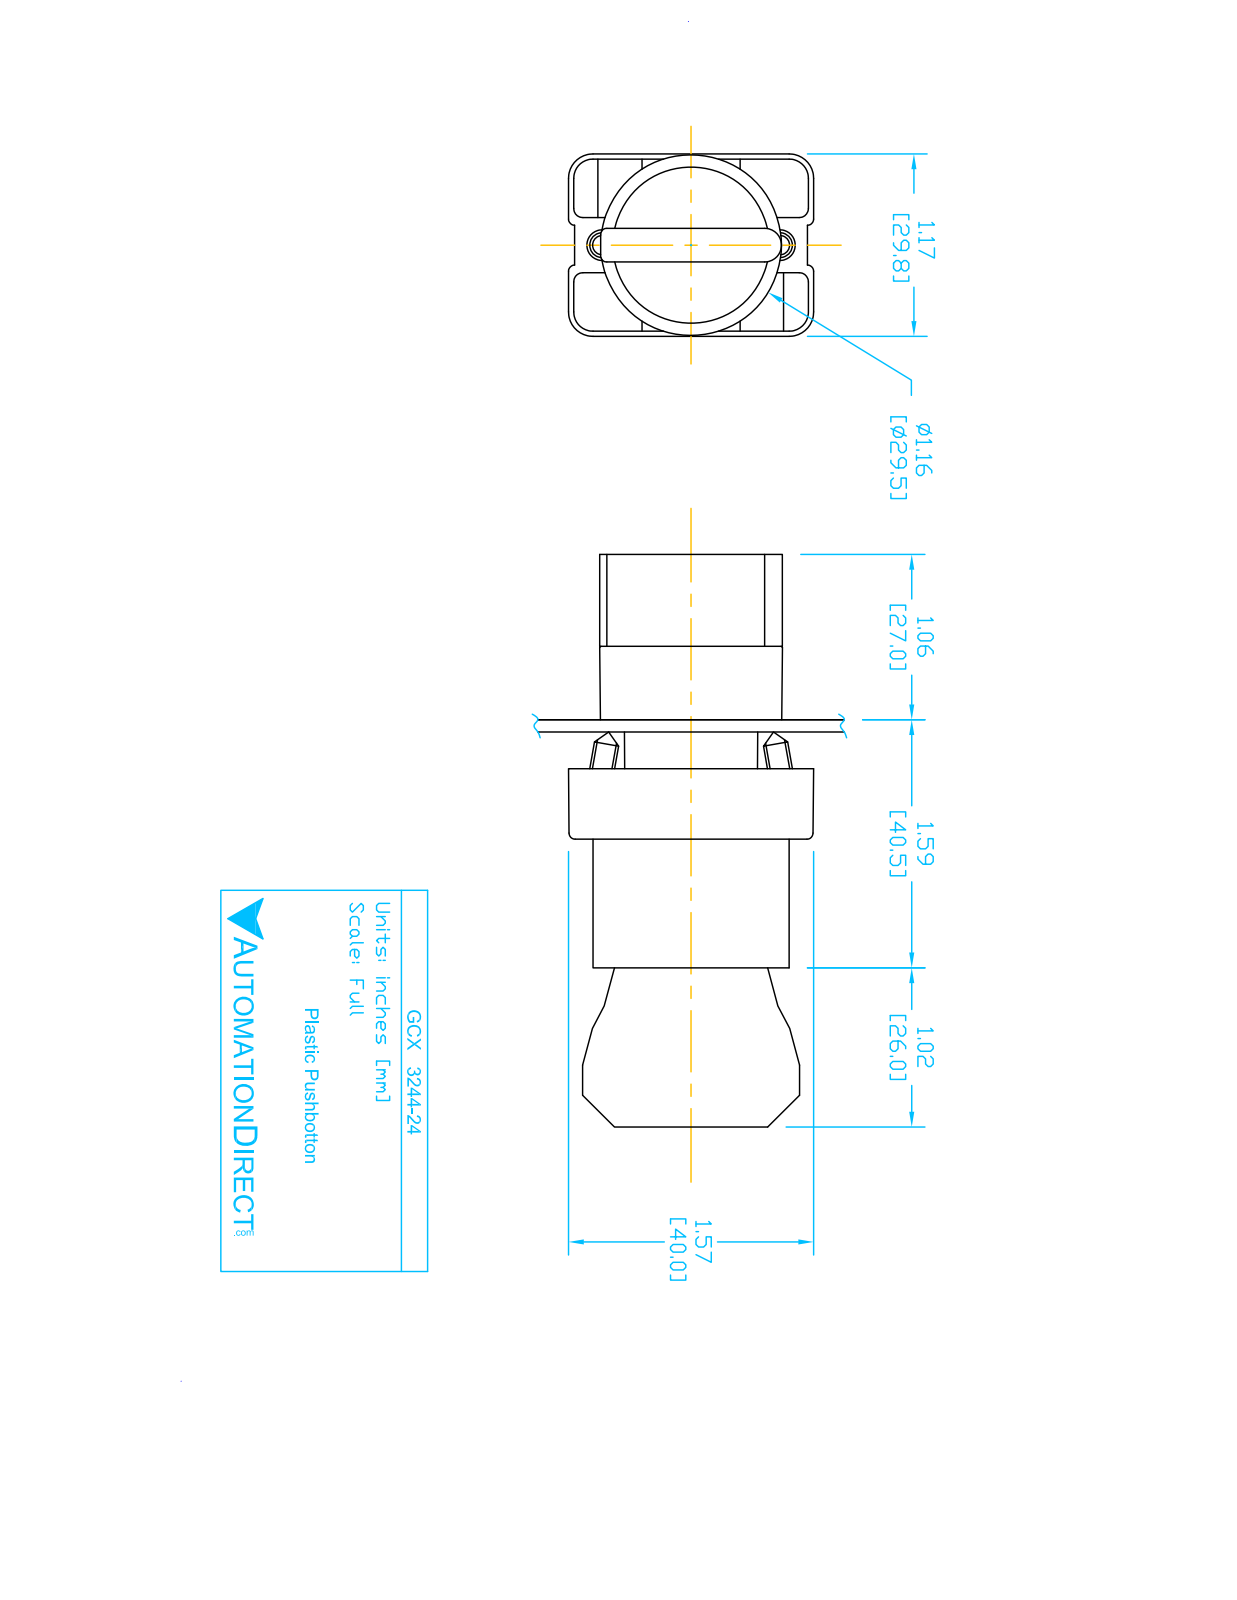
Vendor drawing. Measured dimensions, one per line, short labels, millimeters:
name: ECX3029-2; ecx1040; GCX3244 OPERATOR; GCX3244-24 (+1 more)
written by: SolidWorks 2016 (AUTOMOTIVE_DESIGN)
unit: mm
bodies: 8 solids, 445 faces (263 planar, 151 cylindrical, 31 other)
size: 92.8 × 40.2 × 29.9
volume: 45 870 mm³; area: 25 160 mm²
holes: 2× ⌀2, 2× ⌀3.1, 2× ⌀3.3, 1× ⌀2.2, 1× ⌀5, 1× ⌀11.9, 1× ⌀22.3, 1× ⌀22.6, 1× ⌀26
bosses: 4× ⌀4, 1× ⌀29.8, 1× ⌀25.5, 1× ⌀24, 1× ⌀21.7, 1× ⌀19.8, 1× ⌀12.8
rounds: 24× R1.5, 12× R1, 12× R3.1, 12× R4, 9× R1, 2× R3.3, 1× R0.5, 1× R1.6
face distances: 21, 51.3, 30.3, 14.7, 31.6, 29.7, 12, 11.9, 0.8, 0.8
hole spacings: 6, 13.8, 12, 12.4
